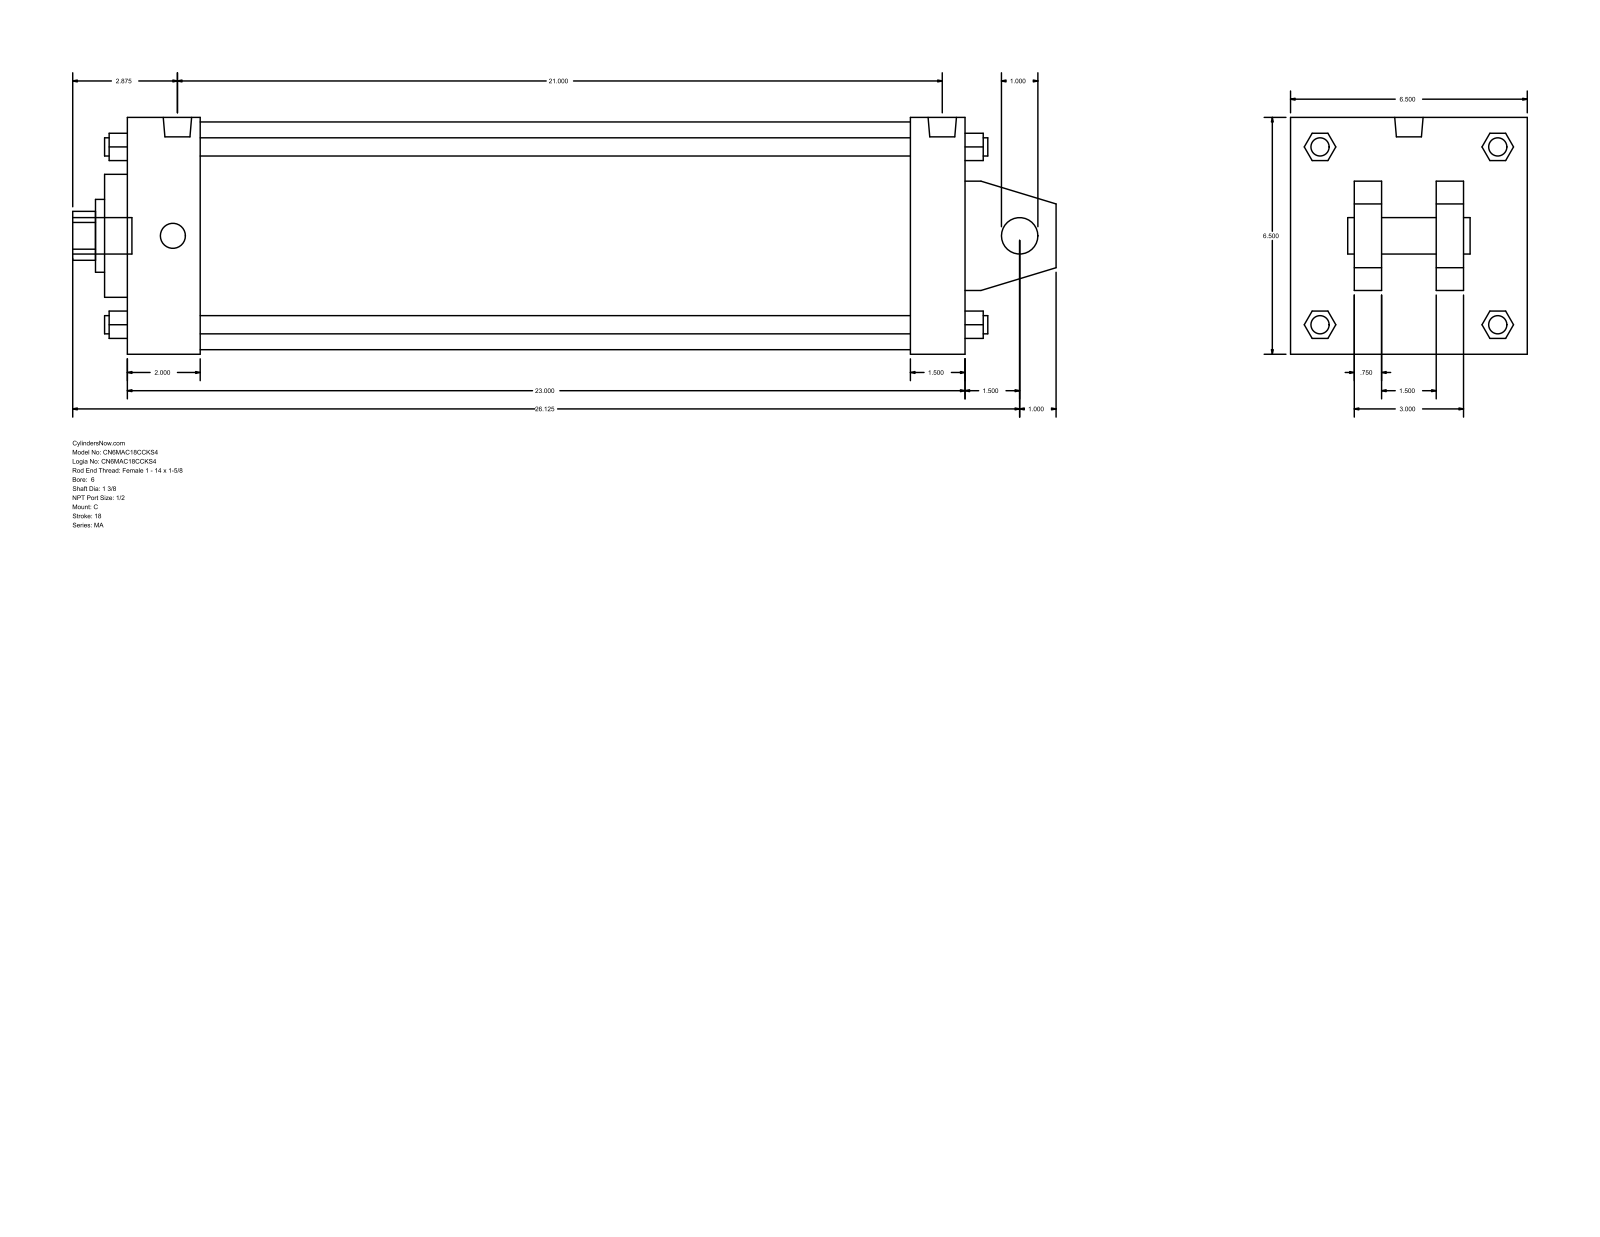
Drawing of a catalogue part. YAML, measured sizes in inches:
part_name: "MA_C__0600_1.375"
step_written_by: "GSSL Pune (CONFIG_CONTROL_DESIGN)"
units: inches
bodies: {solids: 0, faces: 141, planar: 109, cylindrical: 32, other: 0}
overall_size: [27, 6.5, 6.5]
round_holes:
  - {diameter: 1, count: 1}
  - {diameter: 1.375, count: 1}
  - {diameter: 2, count: 1}
  - {diameter: 3.375, count: 1}
  - {diameter: 6.25, count: 1}
round_bosses_or_shafts:
  - {diameter: 0.687, count: 4}
  - {diameter: 0.5, count: 4}
  - {diameter: 0.778, count: 2}
  - {diameter: 1, count: 1}
partial_cylinders:
  - {radius: 0.672, count: 1}
face_to_face_distances: [6.5, 23, 1.5, 0.75, 2.5, 4, 2, 1.75, 4.75, 21.5]
